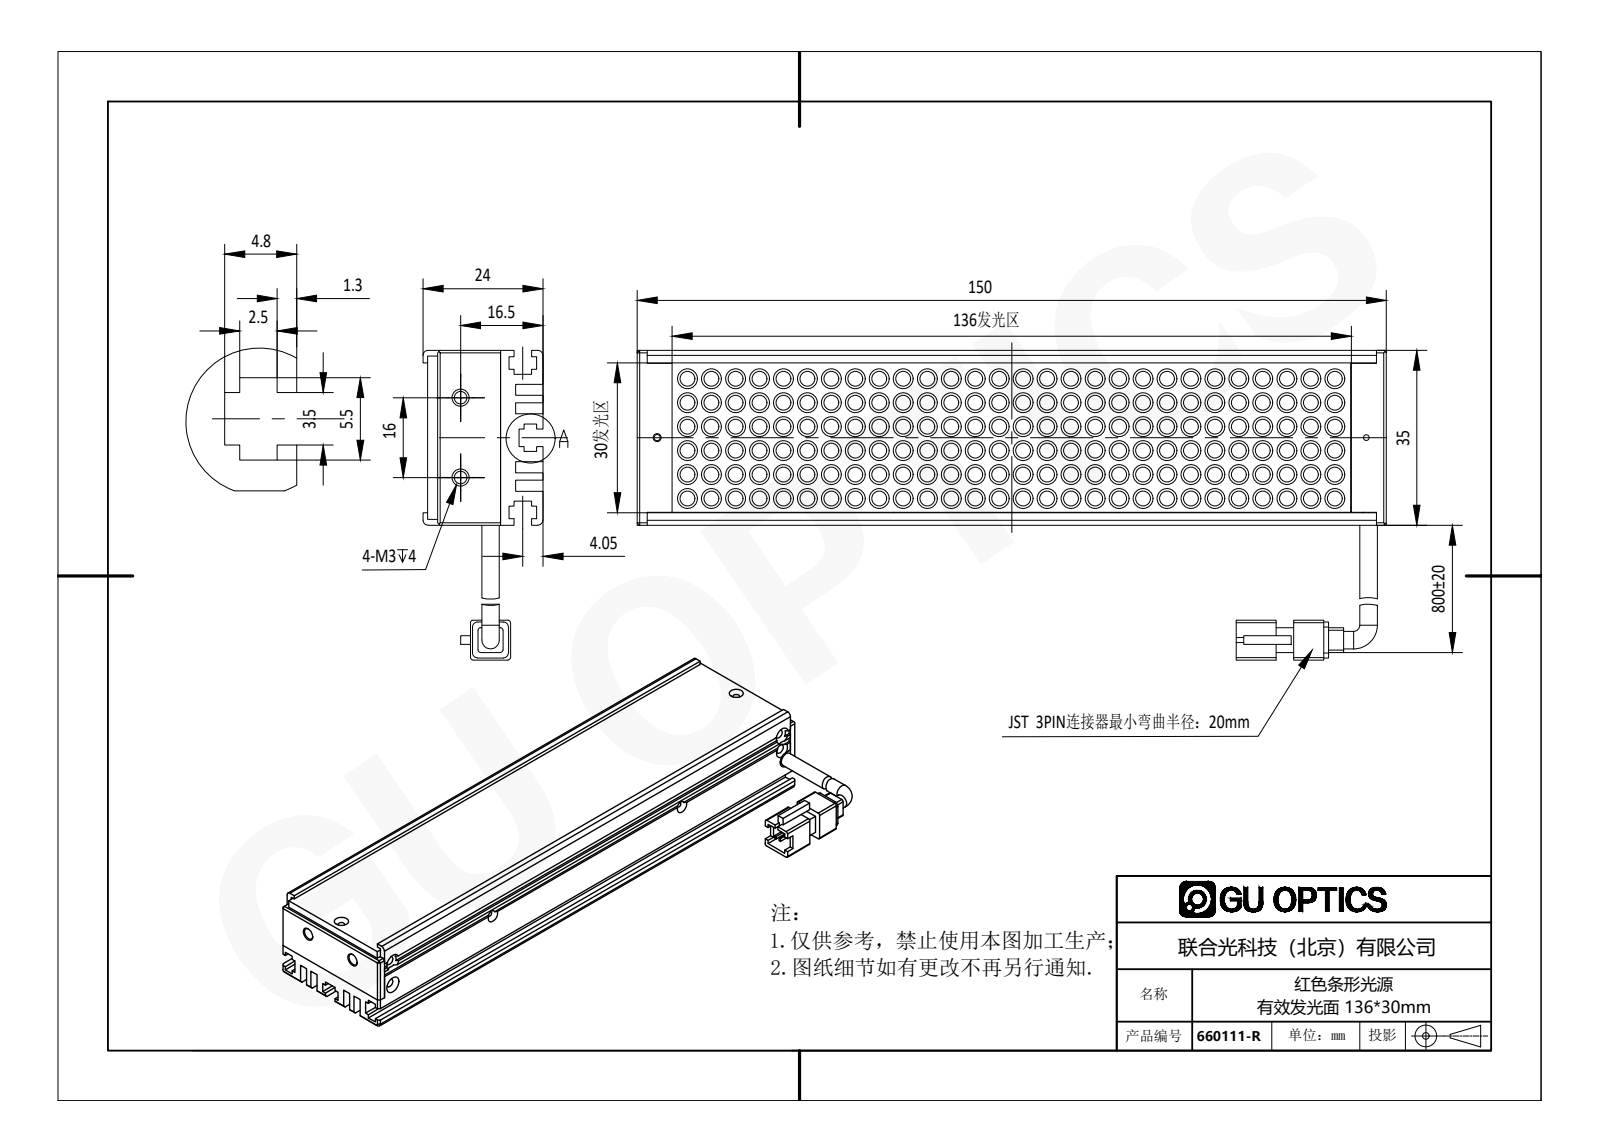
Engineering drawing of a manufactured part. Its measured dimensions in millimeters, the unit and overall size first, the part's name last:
Units: millimetres
Overall size (bounding box): 150 × 62 × 24
Round holes (diameter × count): ⌀1.6 ×5, ⌀1.25 ×4, ⌀2.2 ×4, ⌀1.7 ×2, ⌀2.5 ×2, ⌀3 ×2, ⌀2.4 ×1
Round bosses / shafts (diameter × count): ⌀4 ×168, ⌀3 ×168, ⌀3.5 ×2
Partial cylindrical surfaces — rounded edges, fillets, slot ends (radius × count): R1 ×12, R0.5 ×8, R1.65 ×1
Main face-to-face distances: 12, 8.5, 2, 3.5, 10.5, 14, 1, 2.5, 3.7, 15.5
Hole centre spacings: 7, 36.17, 104.06, 140, 2.5, 4.5, 16, 36
Volume: 66 196 mm³ · Surface area: 68 375 mm²
Bodies: 8 solids, 1543 faces (480 planar, 765 cylindrical, 298 other)
Part name (STEP PRODUCT): 660111-R
STEP written by: SolidWorks 2016 (AUTOMOTIVE_DESIGN)
